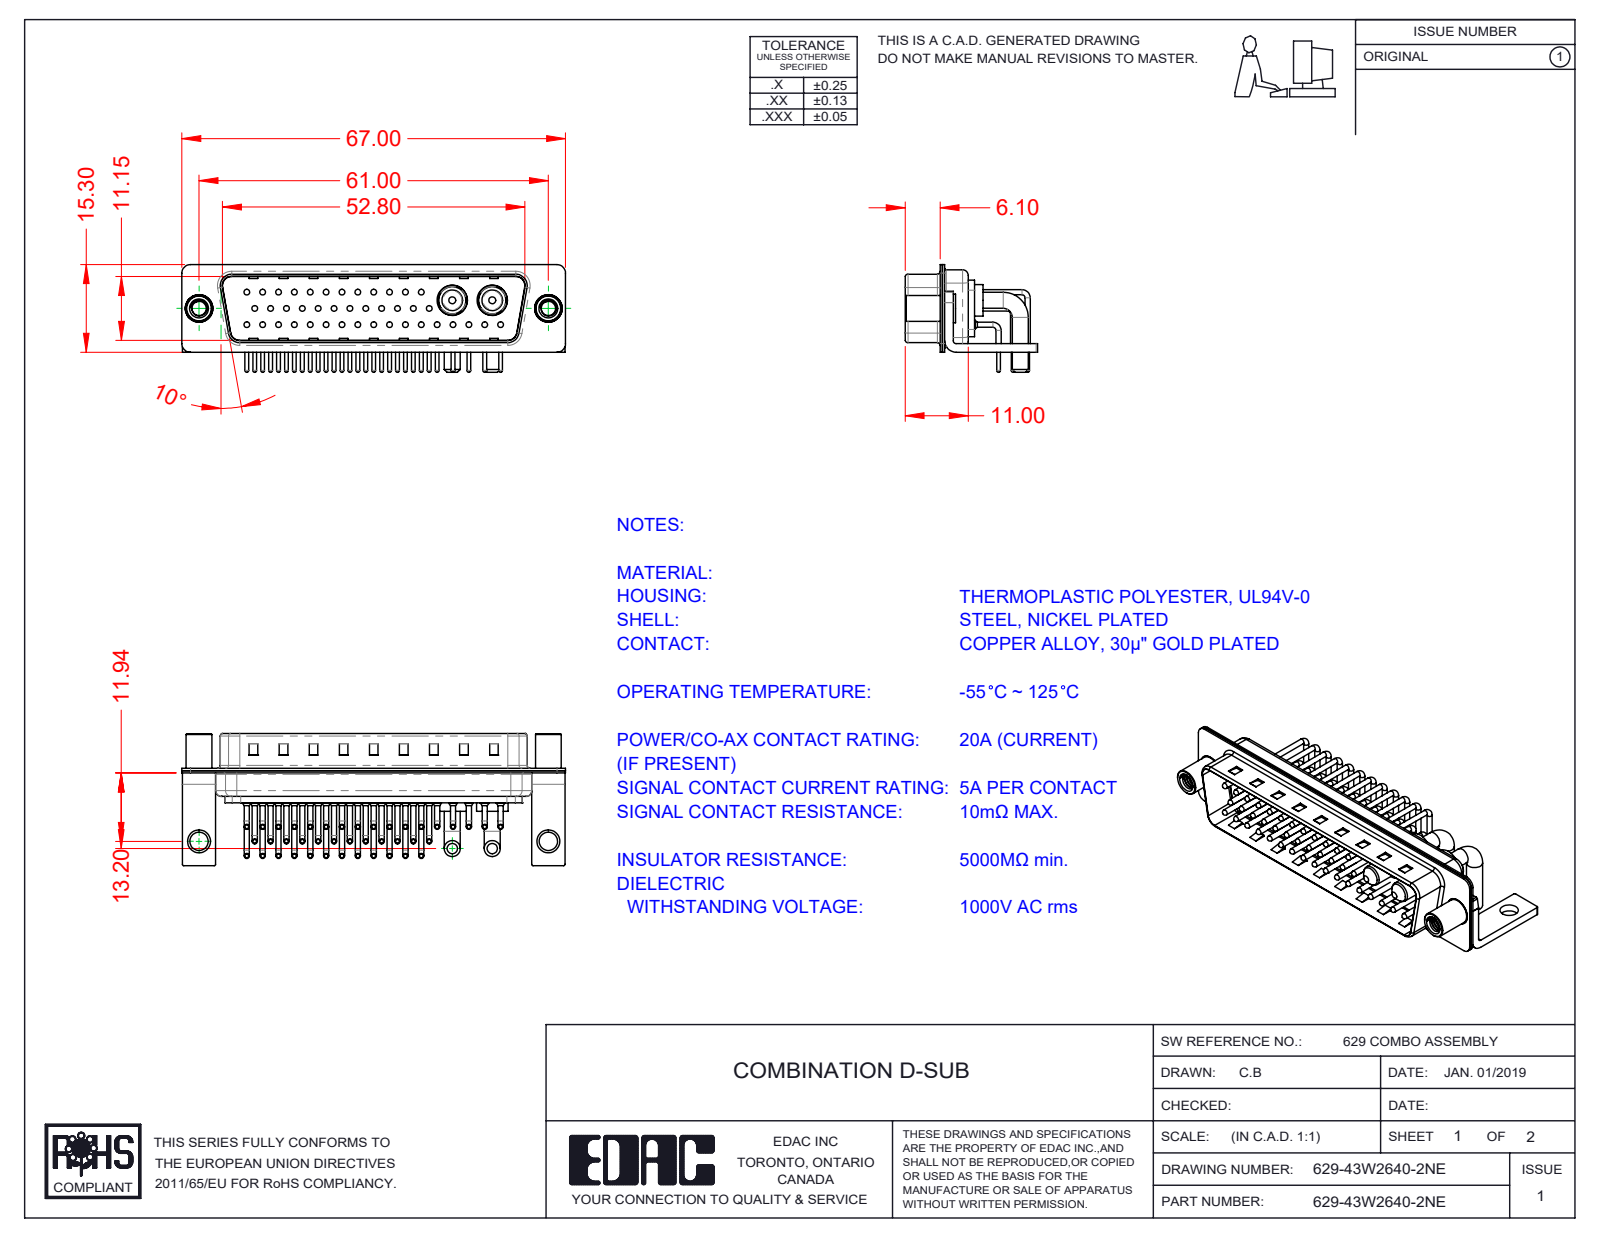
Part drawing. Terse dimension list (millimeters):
name: 629Combo Shell Rear_50 Contacts; 629Combo Contact Row 1_50 Contacts; 629Combo Housing_43W2; 629Combo Stabilizer Bracket_50 Contacts (+6 more)
written by: SolidWorks 2020 (CONFIG_CONTROL_DESIGN)
unit: mm
bodies: 52 solids, 5106 faces (2869 planar, 1731 cylindrical, 506 other)
size: 67 × 23.1 × 18.8
volume: 5 664 mm³; area: 13 626 mm²
holes: 41× ⌀0.75, 41× ⌀1.6, 41× ⌀2, 2× ⌀2.5, 2× ⌀3.2, 2× ⌀4, 2× ⌀4.8, 2× ⌀4.85, 2× ⌀5.3
bosses: 82× ⌀0.9, 41× ⌀1.5, 41× ⌀1, 41× ⌀0.65, 4× ⌀2.8, 2× ⌀5.5, 2× ⌀5.2, 2× ⌀5
rounds: 41× R1.01, 16× R0.25, 16× R1.5, 13× R2, 9× R0.5, 8× R1.6, 4× R0.6, 4× R0.65
face distances: 0.4, 1.5, 11.55, 5.6, 5.2, 0.8, 1.9, 4.1, 6, 0.78
hole spacings: 2.77, 5.54, 3.16, 8.31, 11.08, 13.85, 16.62, 19.39
